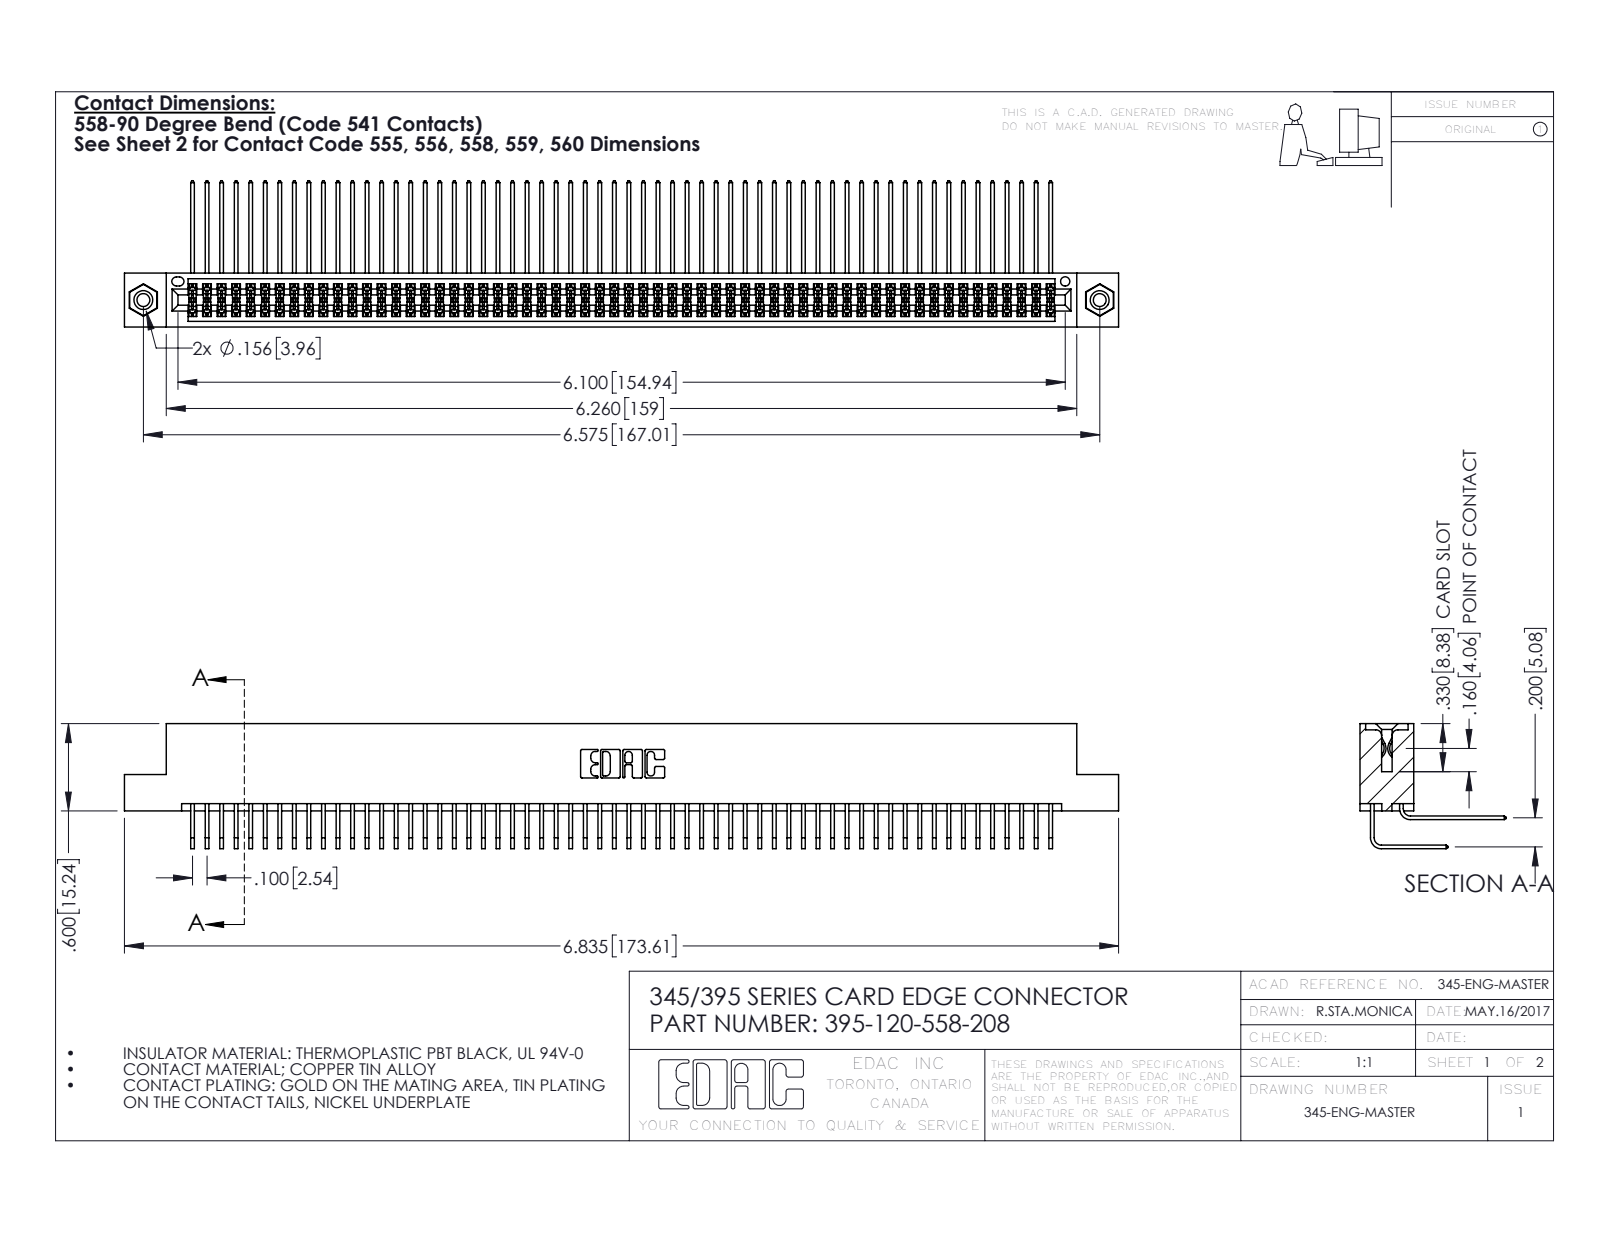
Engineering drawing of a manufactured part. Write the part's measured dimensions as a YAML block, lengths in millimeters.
part_name: "345-250-001_345-250-003-102; 345-292-001_558 559 Tail - 1; 345-292-001_558 Tail - 2; 395-120-558-208 (+1 more)"
step_written_by: "SolidWorks 2016 (CONFIG_CONTROL_DESIGN)"
units: millimeters
bodies: {solids: 123, faces: 6426, planar: 4312, cylindrical: 2098, other: 16}
overall_size: [173.6, 25.5, 21.8]
volume: 17710
surface_area: 29810
round_holes:
  - {diameter: 2.3, count: 2}
  - {diameter: 3.2, count: 2}
  - {diameter: 4, count: 2}
  - {diameter: 1.6, count: 1}
round_bosses_or_shafts:
  - {diameter: 3.9, count: 2}
partial_cylinders:
  - {radius: 0.2, count: 181}
  - {radius: 0.3, count: 22}
  - {radius: 0.2, count: 6}
  - {radius: 0.8, count: 6}
  - {radius: 0.7, count: 3}
  - {radius: 0.4, count: 2}
  - {radius: 0.5, count: 2}
  - {radius: 0.6, count: 2}
face_to_face_distances: [1.8, 7.6, 5.1, 9.4, 2.5, 6.9, 0.6, 5.7, 0.6, 4.4]
hole_center_spacings: [6.9, 161, 167]
